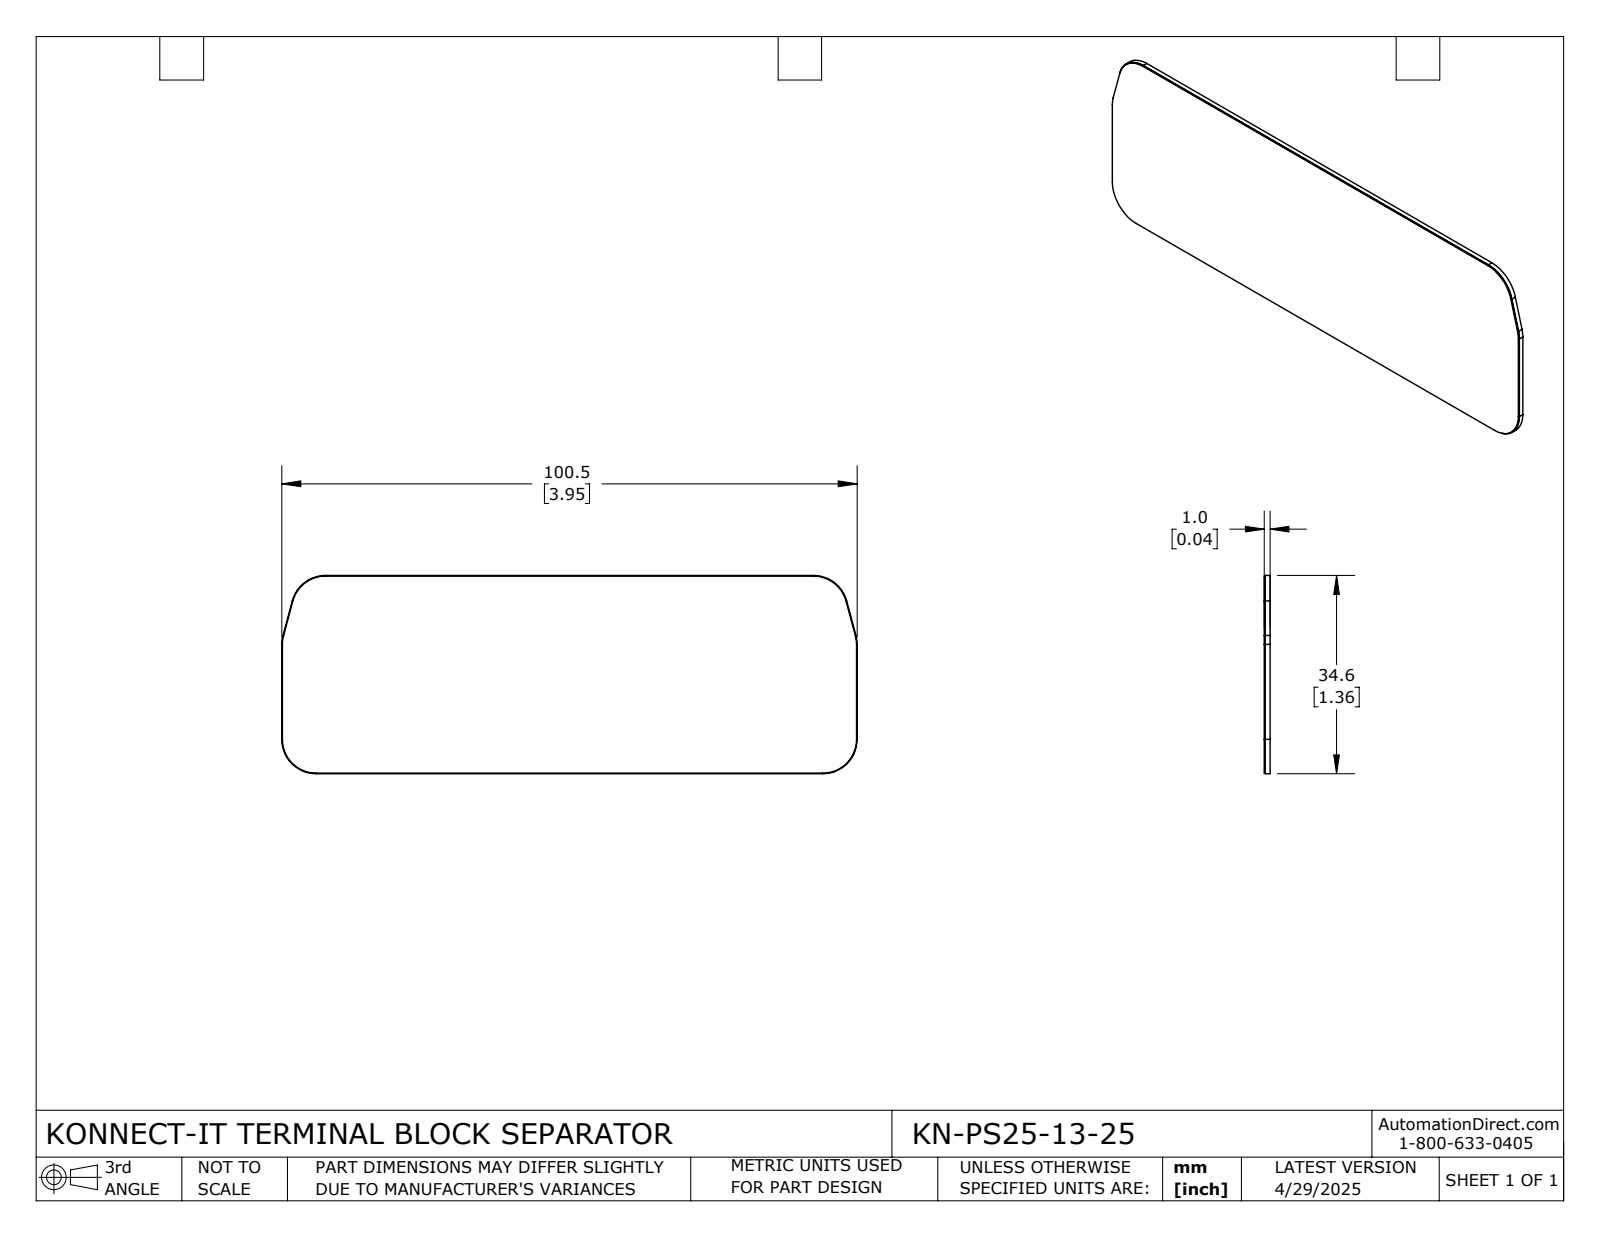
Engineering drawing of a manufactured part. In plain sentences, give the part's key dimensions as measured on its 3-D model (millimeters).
The part is named "KN-PS25-13-25". Its 3-D file was written by "SolidWorks 2024 (CONFIG_CONTROL_DESIGN)". It is 1 solid with 27 faces: 15 planar, 12 cylindrical and 0 other. Overall it measures 100.45 by 34.61 by 1 millimeters. Its volume is 3 415 cubic millimeters and its surface area 7 095 square millimeters. Partial cylindrical surfaces (rounded edges, fillets, slot ends): 6 of radius 5.9, 6 of radius 6. The main face-to-face distances are 1, 34.61, 34.51, 0.85, 100.45, 34.41, 100.35, 100.25.
